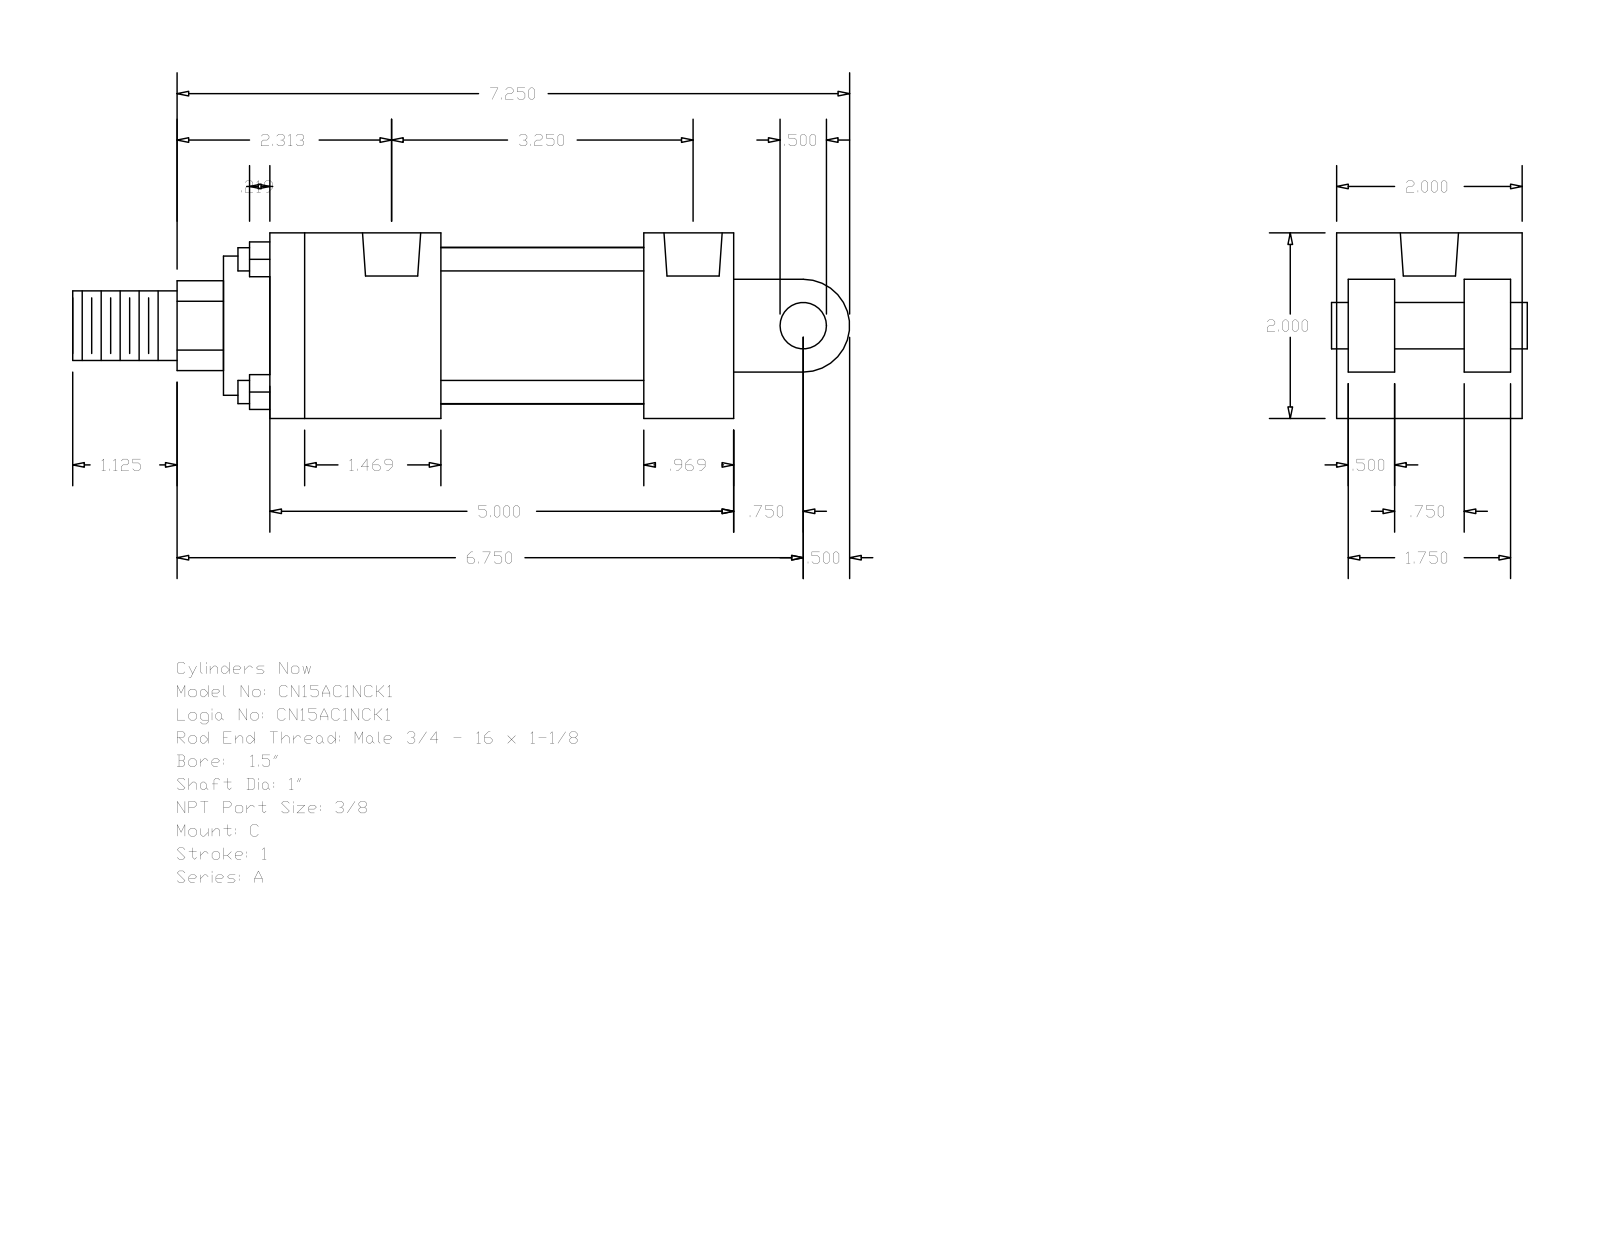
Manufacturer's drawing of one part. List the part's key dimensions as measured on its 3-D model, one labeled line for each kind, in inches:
Part name (STEP PRODUCT): A_C__0150_1
STEP written by: GSSL Pune (CONFIG_CONTROL_DESIGN)
Units: inches
Bodies: 0 solids, 99 faces (70 planar, 29 cylindrical, 0 other)
Overall size (bounding box): 8.375 × 2 × 2
Round holes (diameter × count): ⌀0.219 ×4, ⌀0.627 ×2
Round bosses / shafts (diameter × count): ⌀0.25 ×4, ⌀1.69 ×1, ⌀1.5 ×1, ⌀1 ×1, ⌀0.75 ×1, ⌀0.5 ×1
Partial cylindrical surfaces — rounded edges, fillets, slot ends (radius × count): R0.484 ×1, R0.5 ×1
Main face-to-face distances: 2, 0.5, 0.125, 0.625, 1.875, 1.375, 1.25, 2.187, 5, 1.5
Hole centre spacings: 0.156, 2.937, 3.094, 3.25
